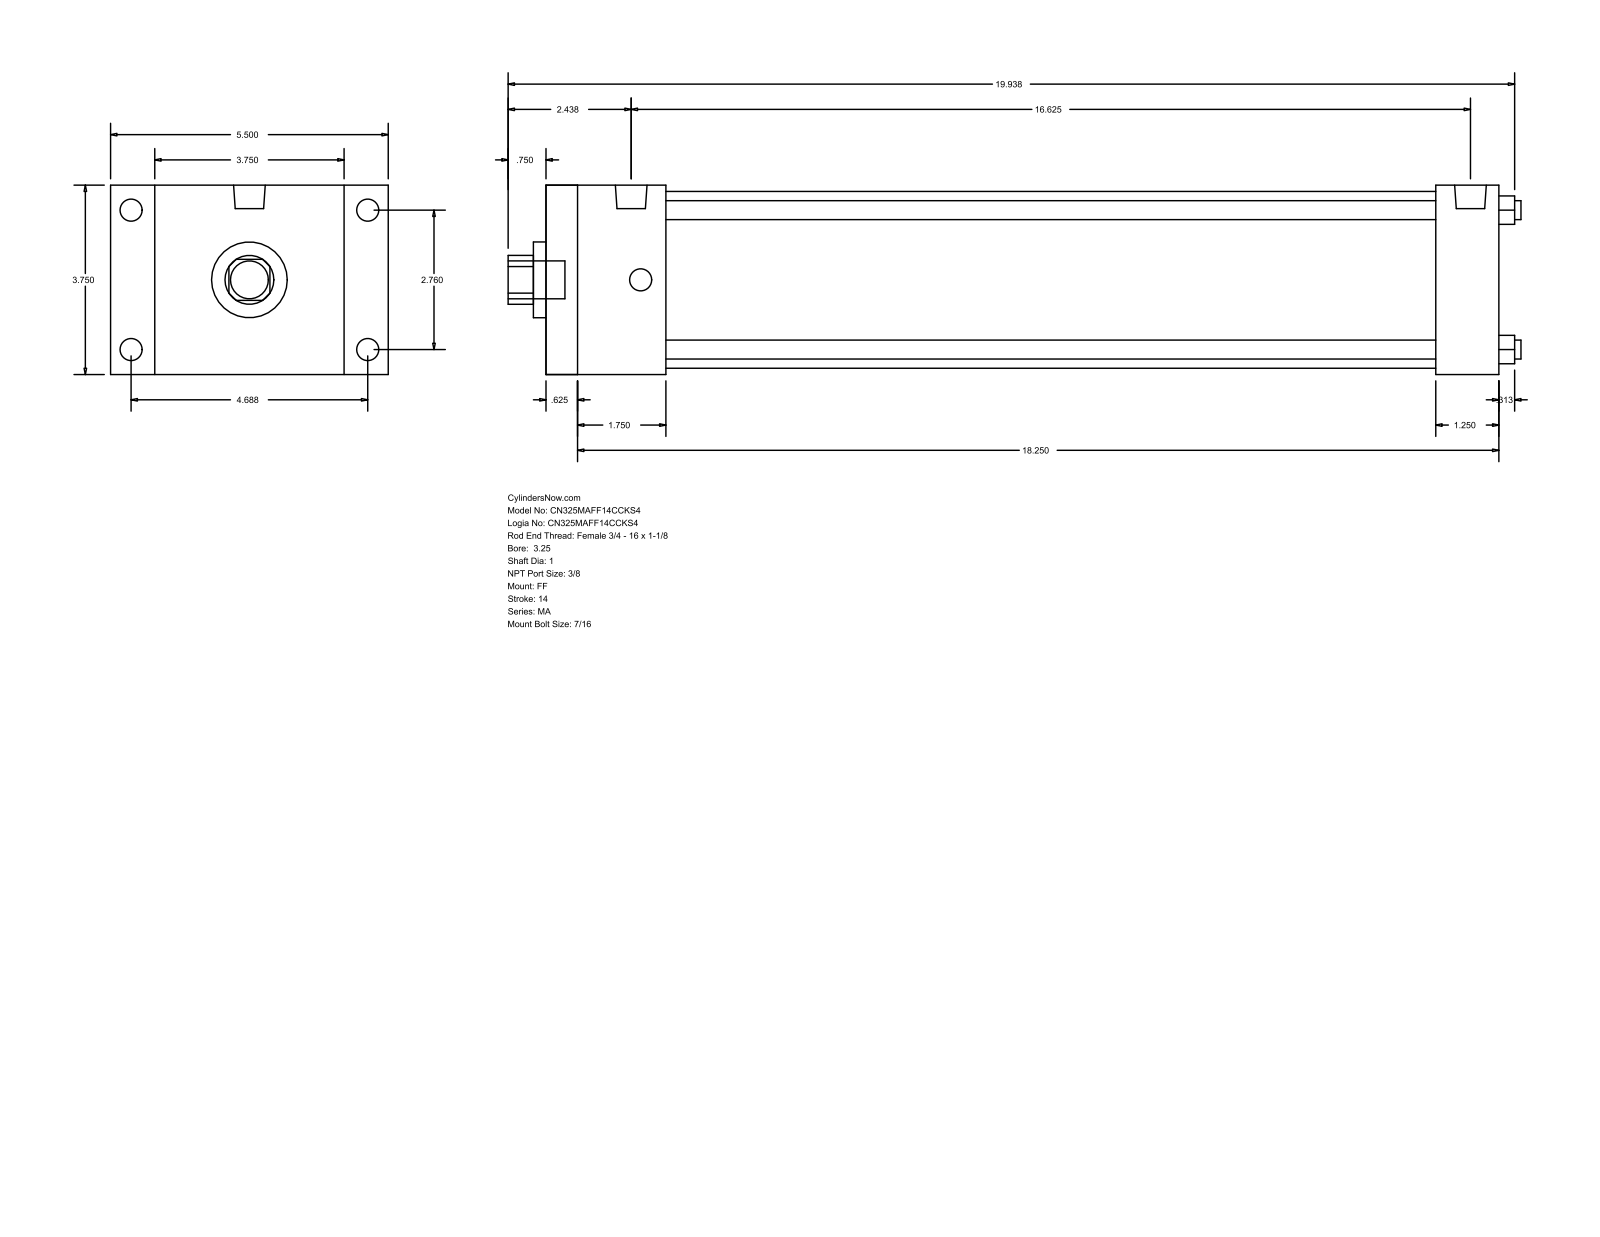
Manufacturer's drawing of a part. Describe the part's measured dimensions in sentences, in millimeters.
The part is named "MA_FF__0325_1". Its 3-D file was written by "GSSL Pune (CONFIG_CONTROL_DESIGN)". It is 0 solids with 92 faces: 64 planar, 28 cylindrical and 0 other. Overall it measures 509.59 by 139.7 by 95.25 millimeters. Round holes: 4 of diameter 9.53, 1 of diameter 25.4, 1 of diameter 38.1, 1 of diameter 88.9. Round bosses or shafts: 8 of diameter 11.11, 2 of diameter 15.93, 1 of diameter 19.05. Partial cylindrical surfaces (rounded edges, fillets, slot ends): 1 of radius 12.29. The main face-to-face distances are 95.24, 479.43, 15.87, 463.56, 22.23, 117.47, 60.33, 447.68, 44.46, 431.81. The hole center spacings are 49.57, 70.1, 99.14.
